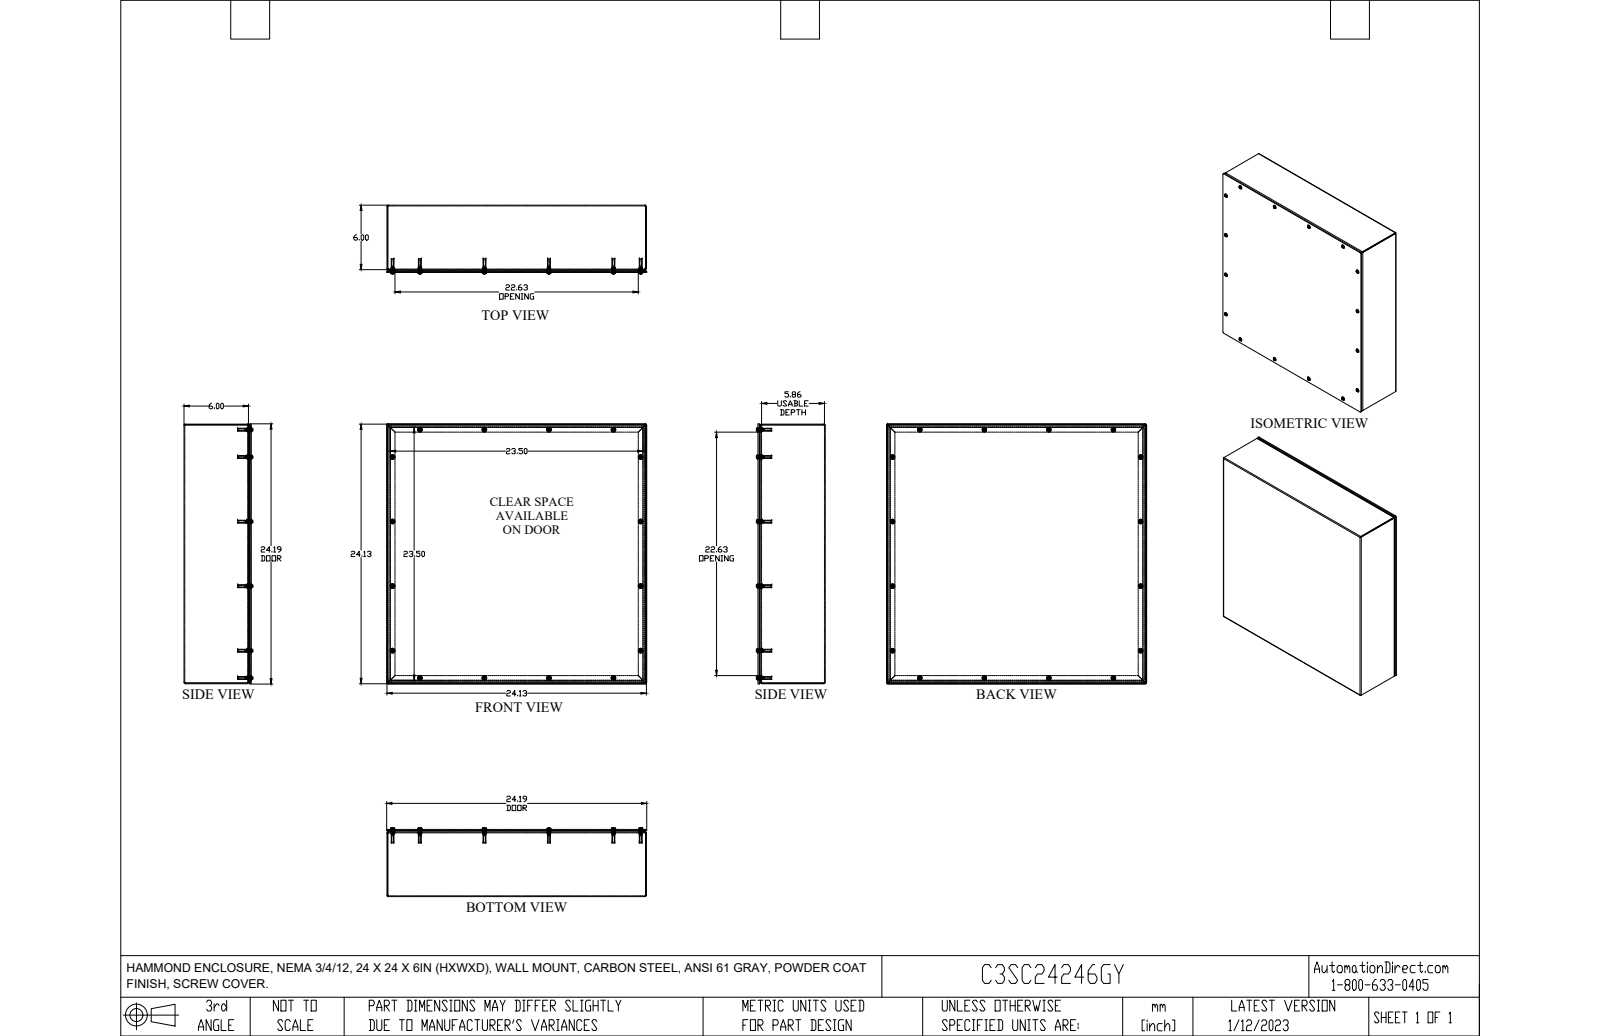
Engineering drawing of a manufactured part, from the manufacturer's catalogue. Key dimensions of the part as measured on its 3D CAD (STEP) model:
Part name (STEP PRODUCT): C3SC24246GY
STEP written by: SolidWorks 2021 (AUTOMOTIVE_DESIGN)
Units: inches
Bodies: 51 solids, 1476 faces (920 planar, 272 cylindrical, 284 other)
Overall size (bounding box): 24.188 × 24.188 × 6.4
Volume: 161 in³ · Surface area: 3 762 in²
Round holes (diameter × count): ⌀0.159 ×16, ⌀0.16 ×16, ⌀0.25 ×16
Round bosses / shafts (diameter × count): ⌀0.44 ×16, ⌀0.39 ×16, ⌀0.275 ×16, ⌀0.24 ×16, ⌀0.19 ×16, ⌀0.148 ×16
Partial cylindrical surfaces — rounded edges, fillets, slot ends (radius × count): R0.16 ×16, R0.04 ×8, R0.11 ×8, R0.125 ×8, R0.126 ×4, R0.374 ×4
Main face-to-face distances: 0.07, 0.125, 6.125, 6.25, 6.18, 6.055, 24.13, 24.06, 0.07, 23.99
Hole centre spacings: 6, 23.842, 8.906, 12, 14.757, 16.859, 20.694, 22.241
